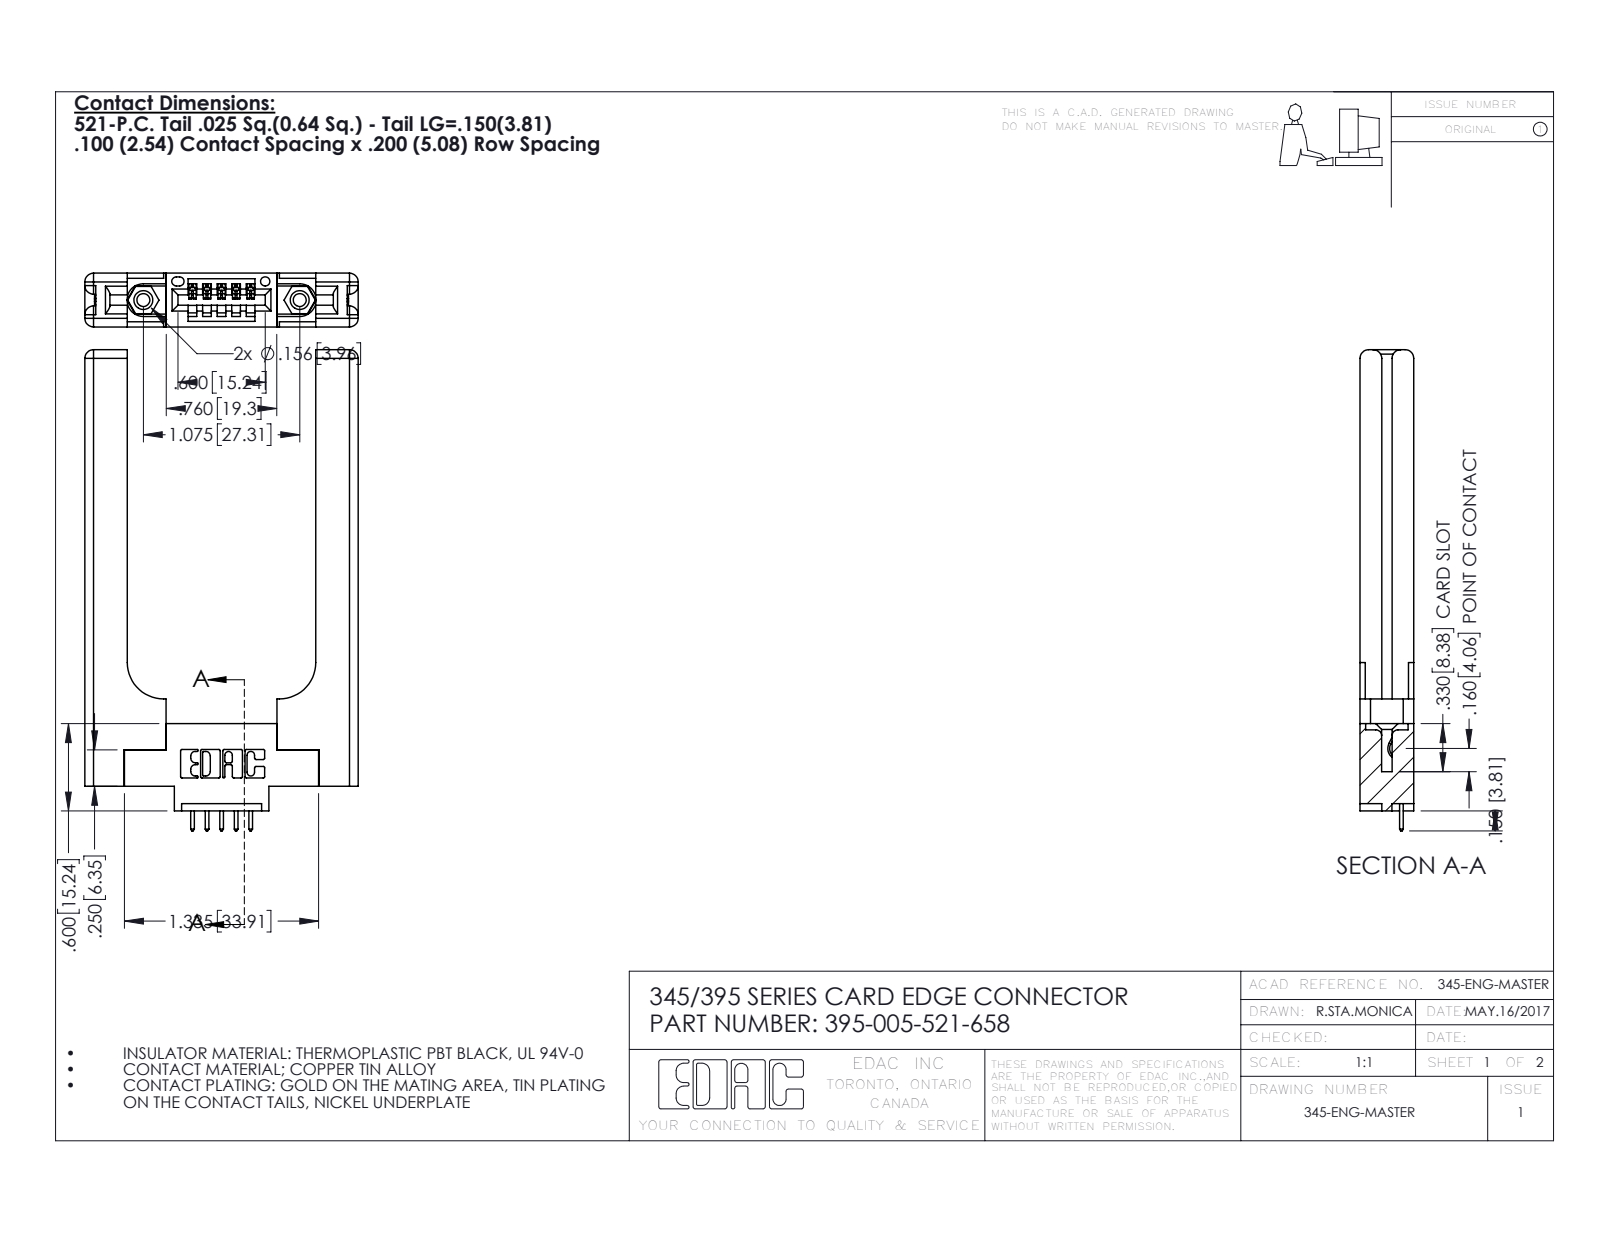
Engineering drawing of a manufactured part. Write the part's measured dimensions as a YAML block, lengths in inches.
part_name: "345 Part_0.170 Offset - 0.156 Dia-TH; 345-220-058_345-220-058; 345-250-001_345-250-001-102; 395-005-521-658 (+1 more)"
step_written_by: "SolidWorks 2016 (CONFIG_CONTROL_DESIGN)"
units: inches
bodies: {solids: 10, faces: 676, planar: 432, cylindrical: 184, other: 60}
overall_size: [3.307, 1.879, 0.37]
volume: 0.769
surface_area: 16
round_holes:
  - {diameter: 0.089, count: 2}
  - {diameter: 0.125, count: 2}
  - {diameter: 0.156, count: 2}
  - {diameter: 0.064, count: 1}
round_bosses_or_shafts:
  - {diameter: 0.155, count: 2}
partial_cylinders:
  - {radius: 0.01, count: 22}
  - {radius: 0.06, count: 16}
  - {radius: 0.006, count: 10}
  - {radius: 0.01, count: 10}
  - {radius: 0.007, count: 6}
  - {radius: 0.031, count: 6}
  - {radius: 0.026, count: 3}
  - {radius: 0.03, count: 2}
face_to_face_distances: [0.37, 0.15, 0.22, 0.072, 1.296, 0.071, 0.148, 0.077, 0.292, 1.587]
hole_center_spacings: [0.27, 0.847, 1.075]
